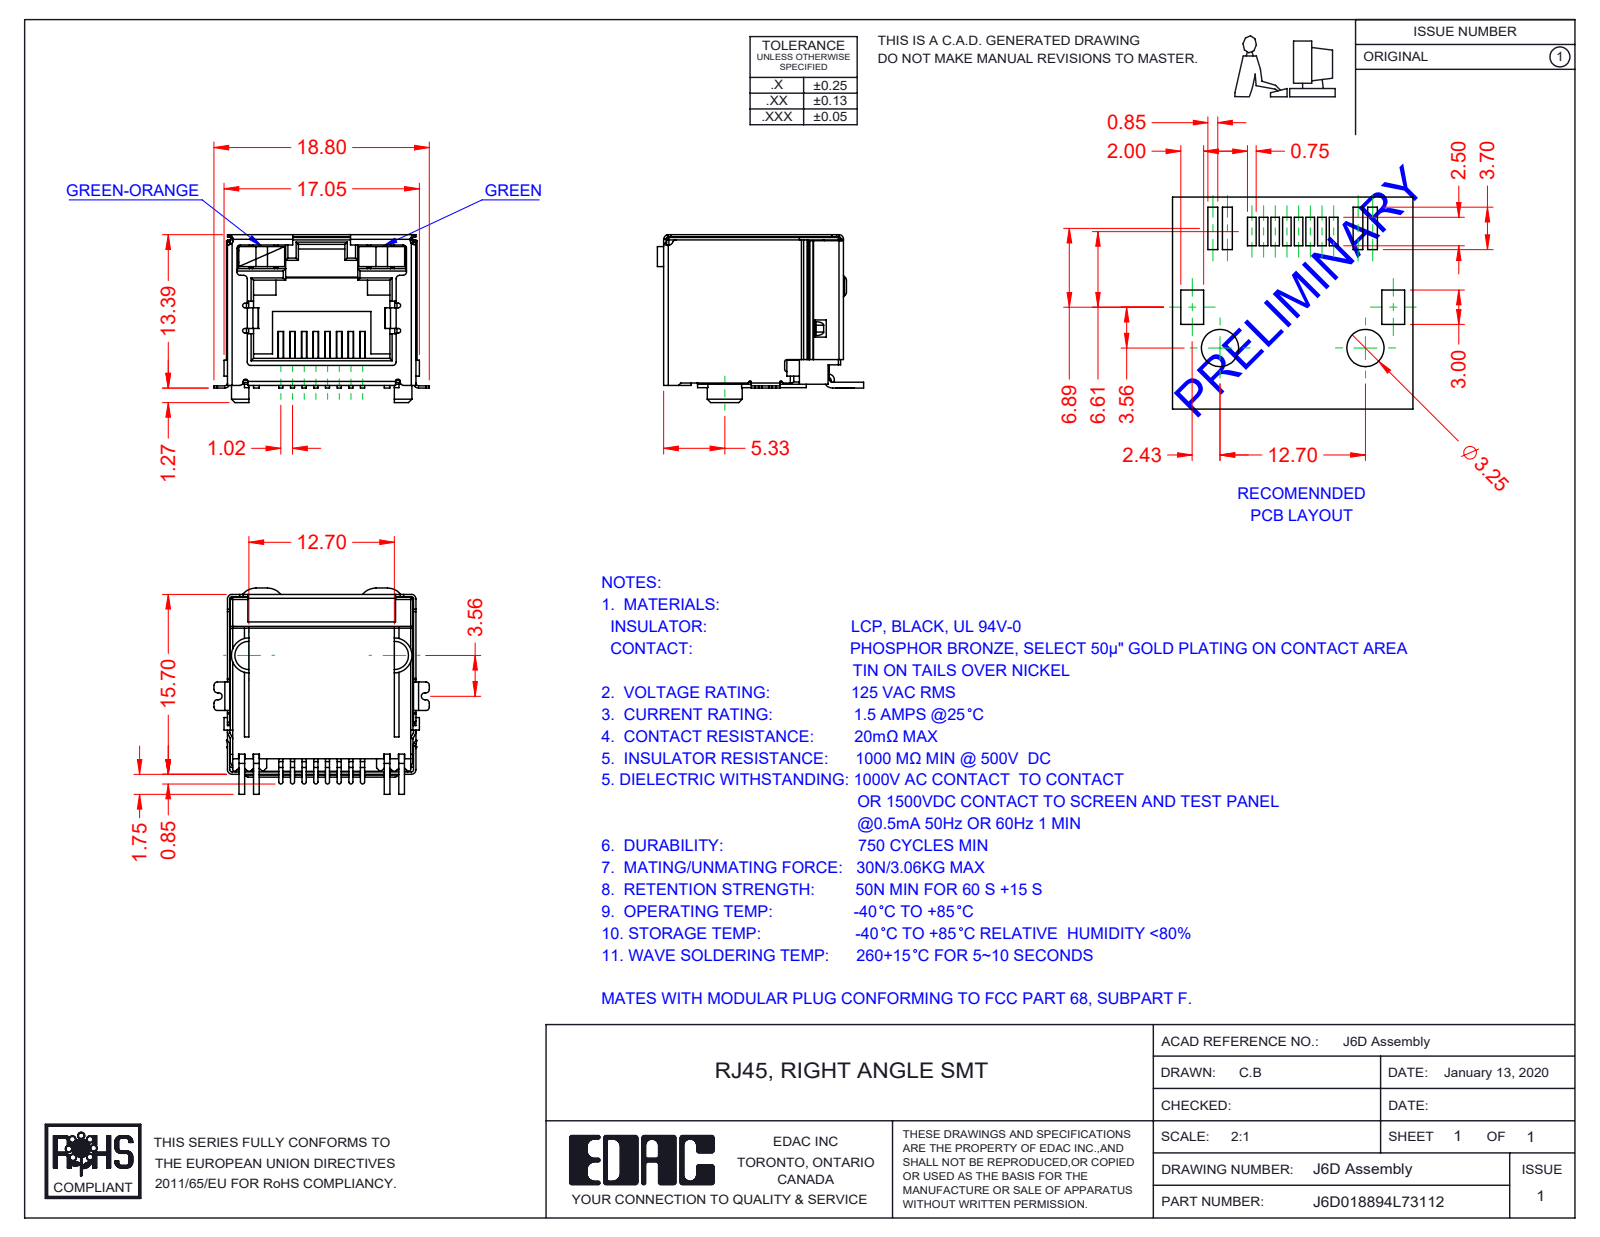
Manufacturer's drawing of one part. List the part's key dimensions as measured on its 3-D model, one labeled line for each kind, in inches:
Part name (STEP PRODUCT): 6D LED LH_7-Green-Orange; 6D Insulator; 6D Shield_LED - No EMI; 6D Contacts (+2 more)
STEP written by: SolidWorks 2016 (CONFIG_CONTROL_DESIGN)
Units: inches
Bodies: 12 solids, 896 faces (645 planar, 218 cylindrical, 33 other)
Overall size (bounding box): 0.74 × 0.709 × 0.577
Volume: 0.11 in³ · Surface area: 7.592 in²
Partial cylindrical surfaces — rounded edges, fillets, slot ends (radius × count): R0.012 ×39, R0.008 ×37, R0.016 ×16, R0.004 ×12, R0.006 ×8, R0.007 ×8, R0.02 ×6, R0.059 ×5
Main face-to-face distances: 0.63, 0.64, 0.638, 0.089, 0.039, 0.628, 0.632, 0.504, 0.018, 0.648
